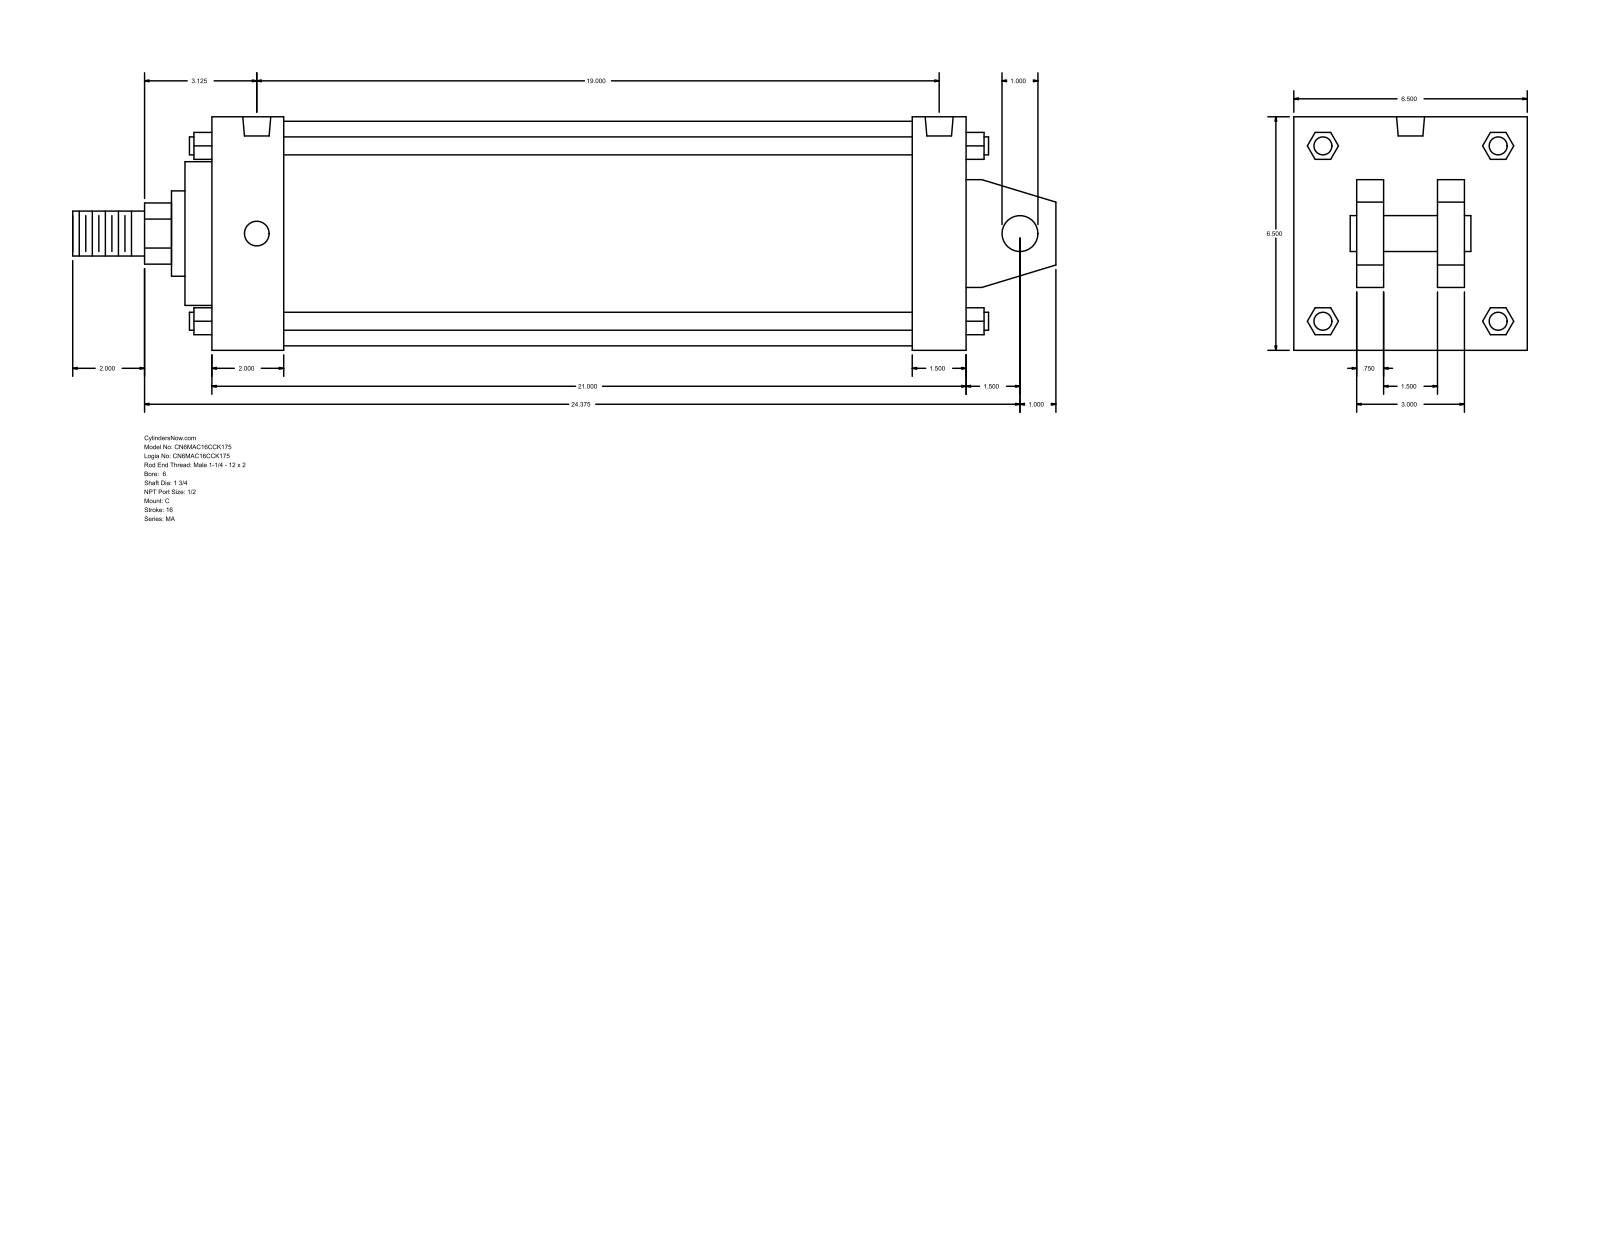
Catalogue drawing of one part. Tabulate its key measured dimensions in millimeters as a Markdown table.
| quantity | value |
| --- | --- |
| part name | MA_C__0600_1.75 |
| STEP written by | GSSL Pune (CONFIG_CONTROL_DESIGN) |
| units | millimeters |
| bodies | 0 solids, 141 faces (109 planar, 32 cylindrical, 0 other) |
| overall size | 695.33 × 165.1 × 165.1 |
| round holes (diameter × count) | 17.46 × 4, 19.77 × 2 |
| round bosses / shafts (diameter × count) | 12.7 × 4, 158.75 × 1, 101.6 × 1, 60.33 × 1, 44.45 × 1, 31.75 × 1, 25.4 × 1 |
| partial cylindrical surfaces (radius × count) | 21.63 × 1 |
| main face-to-face distances | 165.1, 533.4, 19.05, 38.1, 63.5, 101.6, 44.45, 120.65, 57.15, 50.8 |
| hole center spacings | 482.6 |
